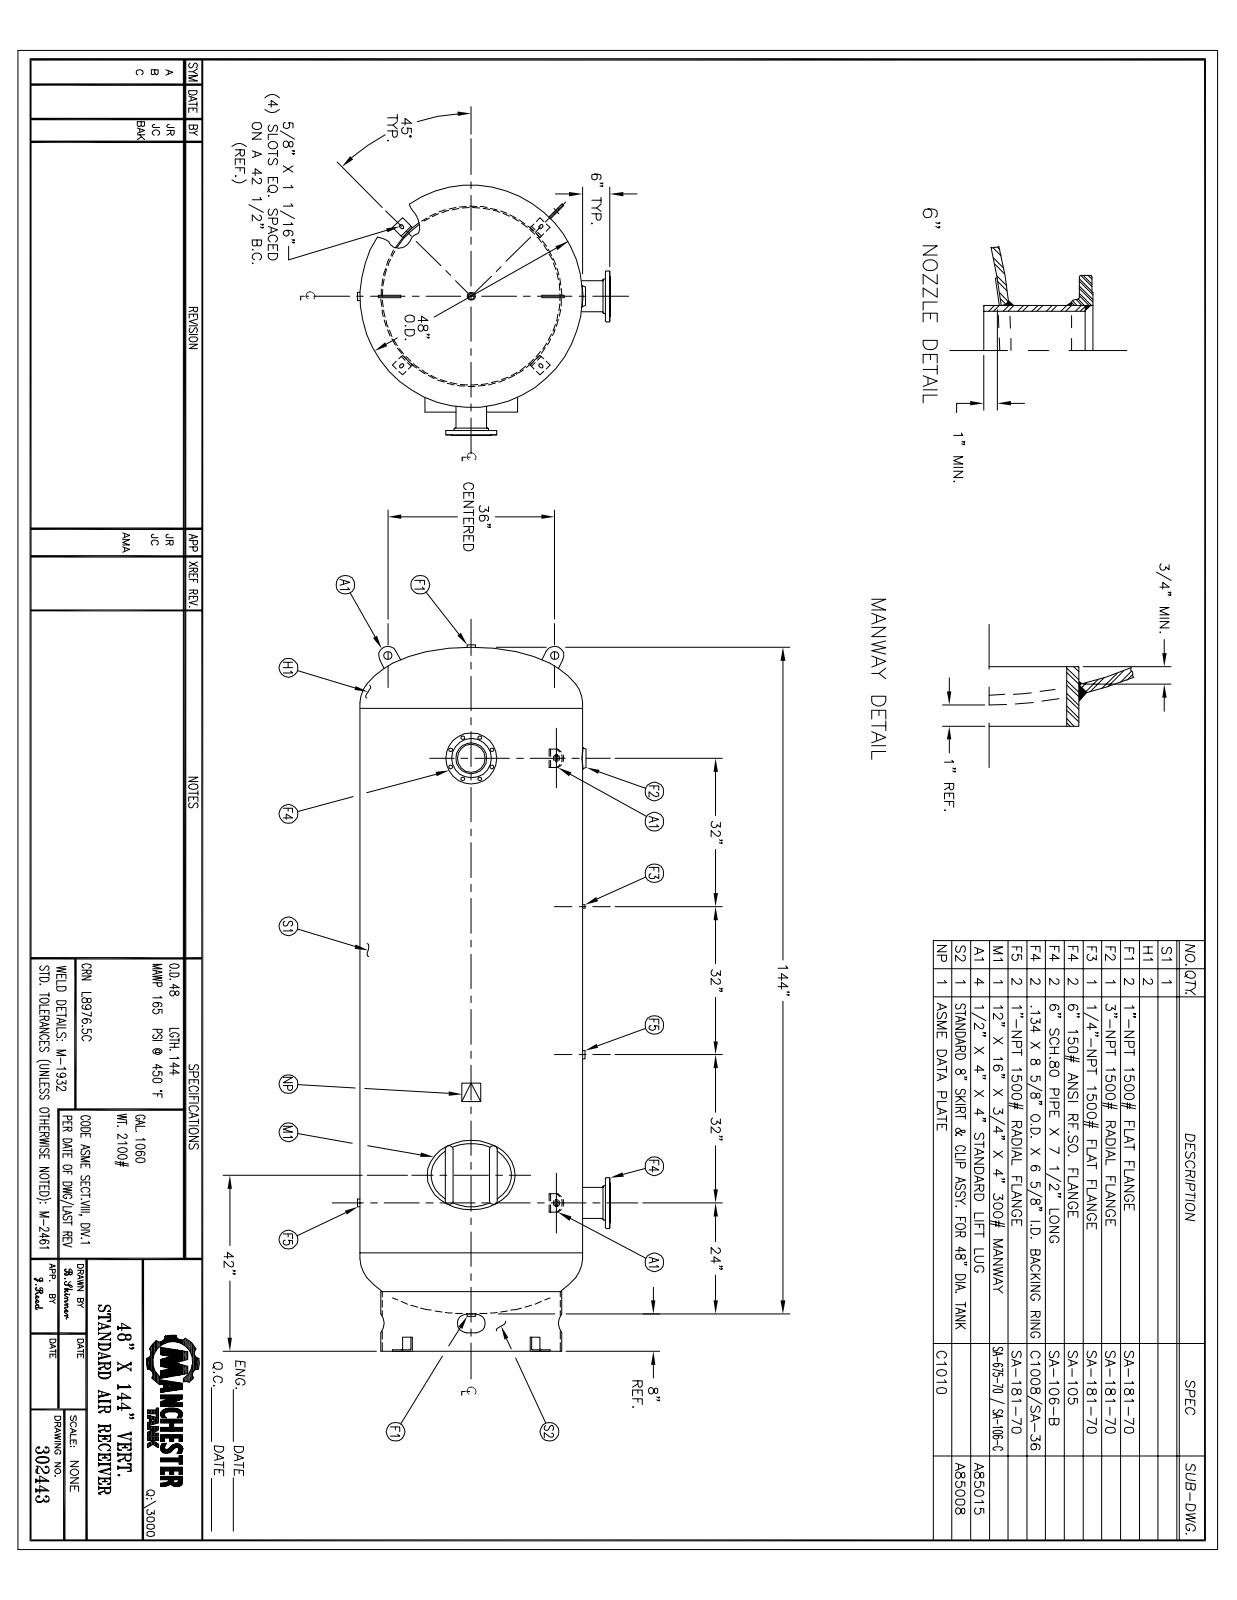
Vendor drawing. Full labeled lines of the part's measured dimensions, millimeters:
Part name (STEP PRODUCT): 302443
STEP written by: SolidWorks 2011 (CONFIG_CONTROL_DESIGN)
Units: millimetres
Bodies: 0 solids, 368 faces (133 planar, 154 cylindrical, 81 other)
Overall size (bounding box): 3883.6 × 1390.7 × 1381
Round holes (diameter × count): ⌀22.2 ×16, ⌀34.9 ×4, ⌀33.4 ×2, ⌀146.3 ×2, ⌀170.7 ×2, ⌀13.7 ×1, ⌀33.4 ×1, ⌀88.9 ×1, ⌀974.8 ×1, ⌀1206.5 ×1
Round bosses / shafts (diameter × count): ⌀279.4 ×2, ⌀215.9 ×2, ⌀168.3 ×2, ⌀60.3 ×2, ⌀25.4 ×2, ⌀1219.2 ×1, ⌀1204.7 ×1, ⌀990.6 ×1
Partial cylindrical surfaces — rounded edges, fillets, slot ends (radius × count): R6.5 ×8, R7.9 ×6, R9.5 ×4, R14.3 ×4, R33.5 ×4, R50.8 ×4, R8 ×2, R150.3 ×1
Main face-to-face distances: 101.6, 23.8, 12.7, 203.2, 25.4, 1.6, 323.9, 3206.9, 546.2, 222.4
Hole centre spacings: 170.6, 222.9, 120.7, 92.3, 92.4, 241.3, 120.7, 812.8
